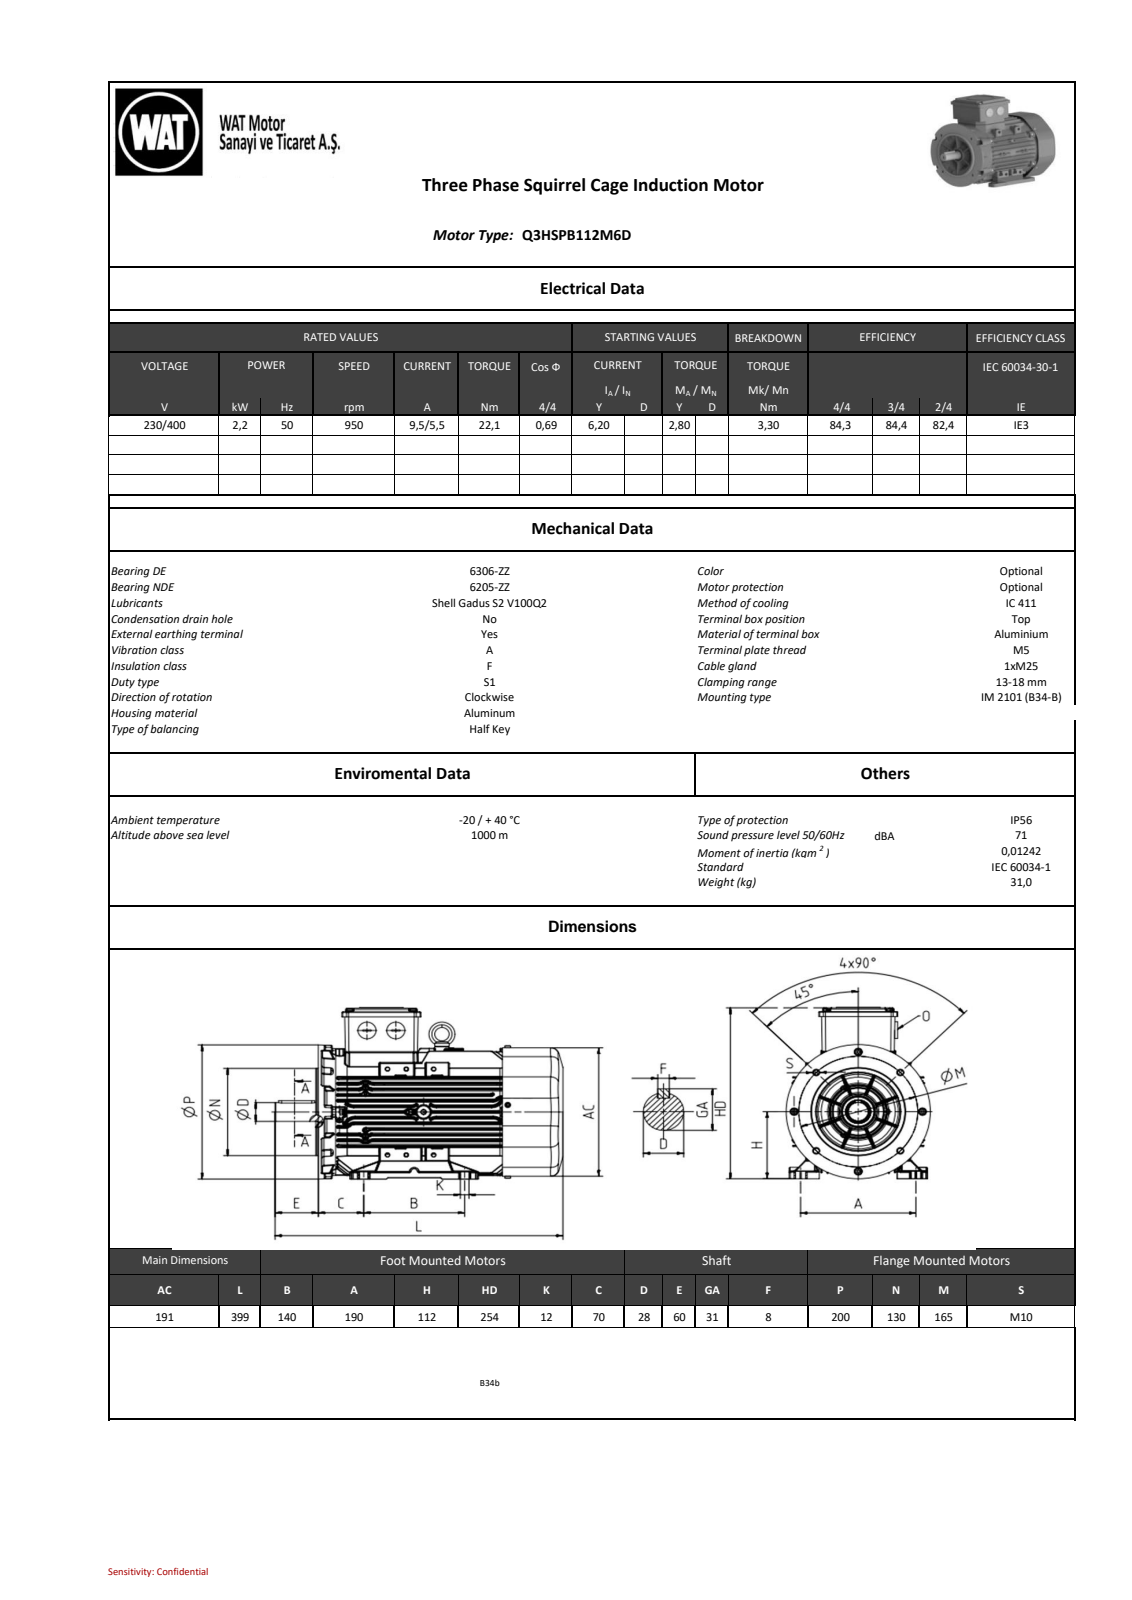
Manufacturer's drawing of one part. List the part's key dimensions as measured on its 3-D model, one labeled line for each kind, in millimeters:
Part name (STEP PRODUCT): QHS Series_ 112_B14b_stp_objects
STEP written by: SIEMENS PLM Software NX2206.8101 (AUTOMOTIVE_DESIGN)
Units: millimetres
Bodies: 0 solids, 5562 faces (1196 planar, 2196 cylindrical, 2170 other)
Overall size (bounding box): 399.31 × 243.22 × 200
Round holes (diameter × count): ⌀8.5 ×4, ⌀4.72 ×1, ⌀10 ×1, ⌀44.42 ×1, ⌀57.4 ×1, ⌀89 ×1, ⌀109 ×1, ⌀129 ×1, ⌀133 ×1
Round bosses / shafts (diameter × count): ⌀8 ×8, ⌀5 ×4, ⌀25 ×3, ⌀130 ×1, ⌀113.5 ×1, ⌀93.5 ×1, ⌀60.74 ×1, ⌀30 ×1
Partial cylindrical surfaces — rounded edges, fillets, slot ends (radius × count): R0.8 ×617, R1 ×585, R0.5 ×77, R2 ×77, R0.81 ×51, R5 ×40, R15 ×26, R3 ×16
Main face-to-face distances: 8.53, 8.46, 8.45, 76.24, 16.91, 93.45, 25.58, 17.05, 76.68, 59.63
Hole centre spacings: 82.51, 116.68, 165.01
